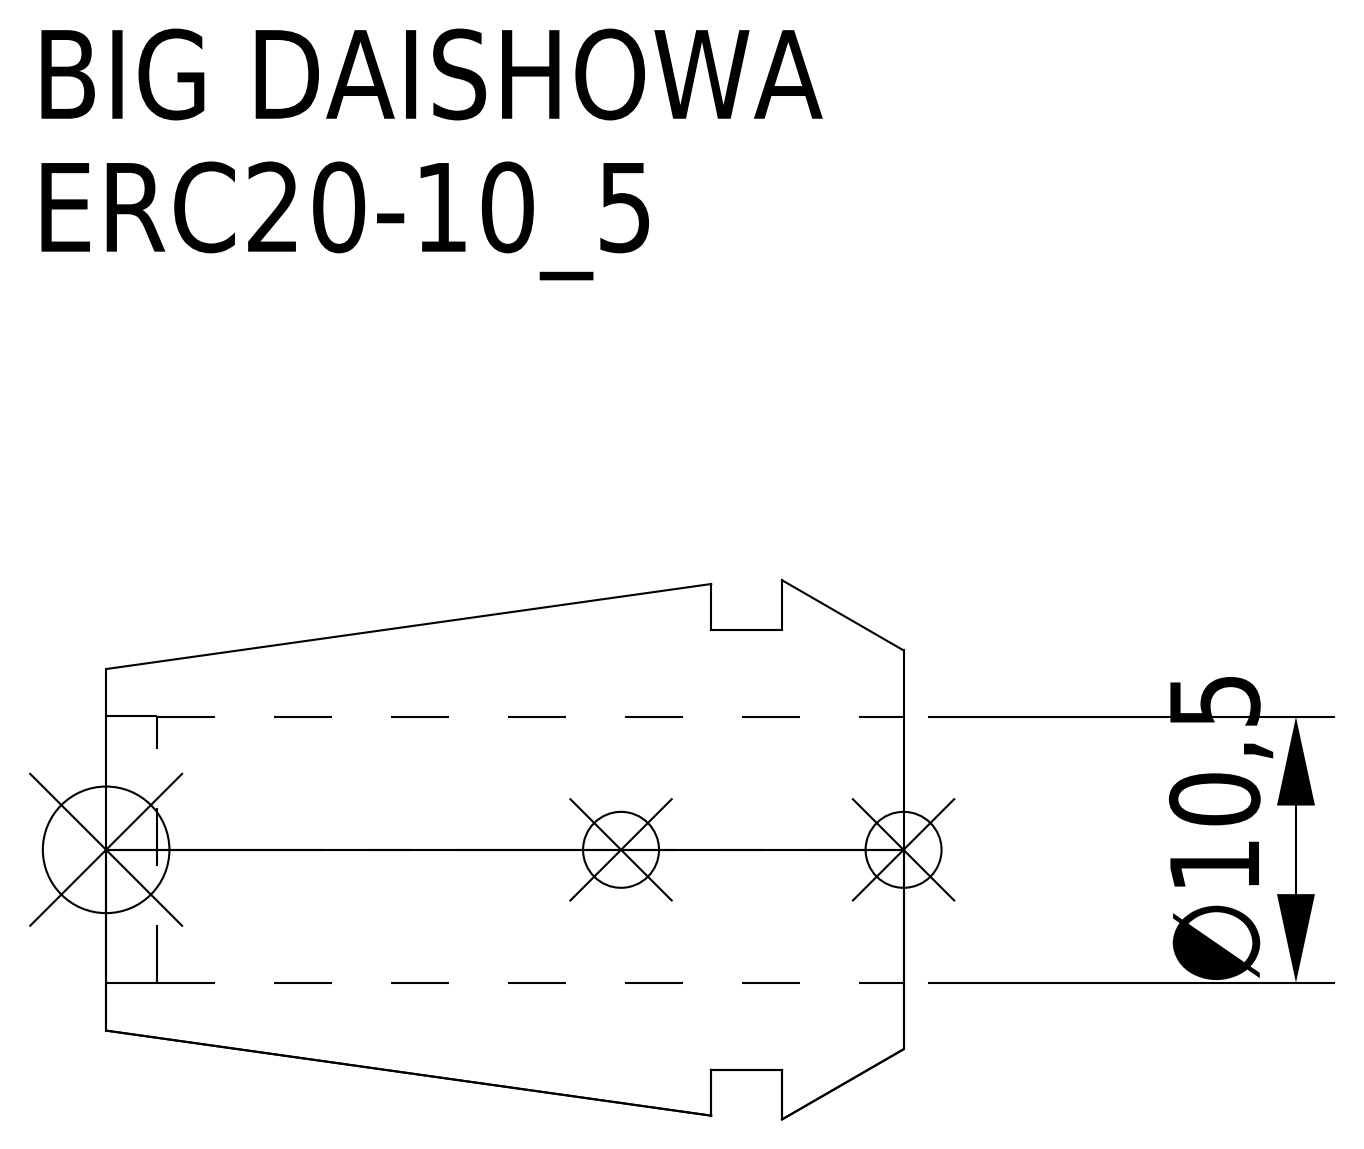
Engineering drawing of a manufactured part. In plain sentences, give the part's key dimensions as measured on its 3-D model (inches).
The part is named "ERC20-10_5". Its 3-D file was written by "CREO PARAMETRIC BY PTC INC, 2016380 (AUTOMOTIVE_DESIGN)". It is 1 solid with 15 faces: 5 planar, 6 cylindrical and 4 other. Overall it measures 1.24 by 0.839 by 0.839 inches. Its volume is 0.314 cubic inches and its surface area 5.056 square inches. Round holes: 1 of diameter 0.413, 1 of diameter 0.415. Round bosses or shafts: 1 of diameter 0.685. The main face-to-face distances are 0.11, 0.189, 0.299, 1.24, 1.051, 0.941, 1.161, 0.972, 0.862, 0.079.
